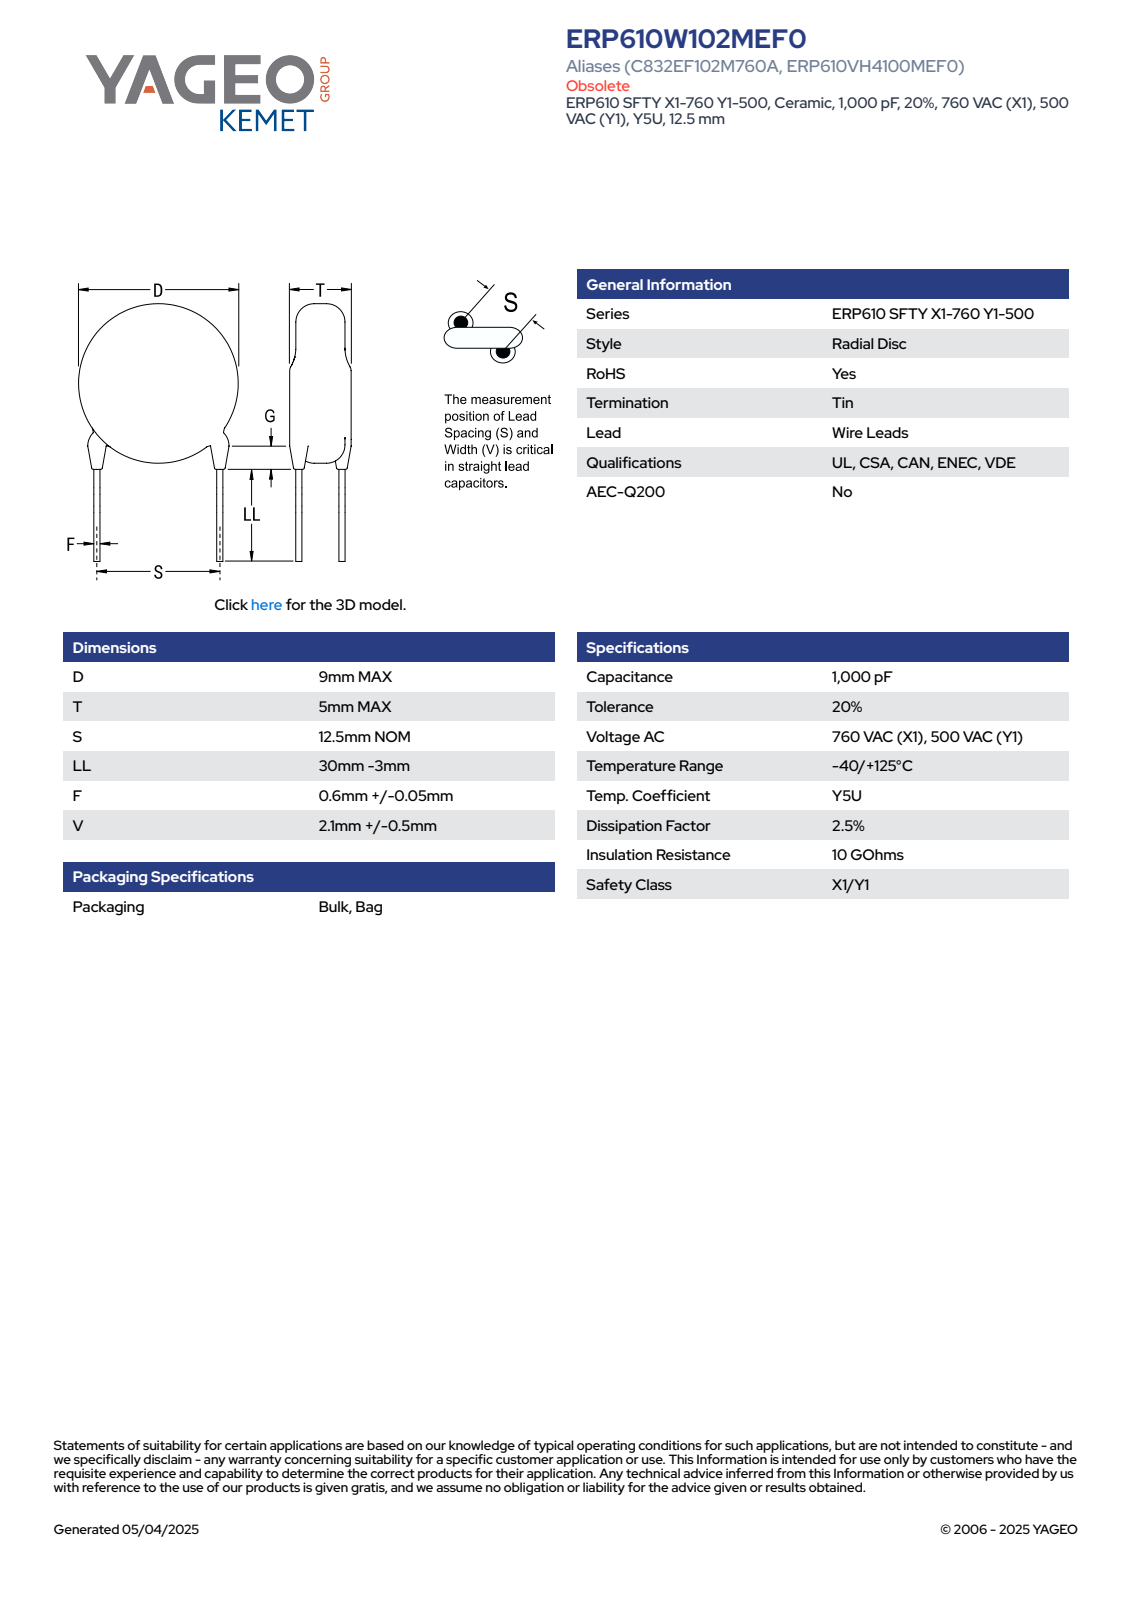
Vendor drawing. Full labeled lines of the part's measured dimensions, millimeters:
Part name (STEP PRODUCT): CCD_KST_9X5_D9T5S12.5LL27F0.65G3V2.6
STEP written by: SolidWorks 2014 (AUTOMOTIVE_DESIGN)
Units: millimetres
Bodies: 4 solids, 81 faces (63 planar, 6 cylindrical, 12 other)
Overall size (bounding box): 36.24 × 12.88 × 5
Volume: 330 mm³ · Surface area: 381 mm²
Round bosses / shafts (diameter × count): ⌀0.65 ×2, ⌀9 ×1
Main face-to-face distances: 5, 32.3, 31.18, 1.12, 0.49, 1.26, 0.91, 0.7, 0.42, 2.31
